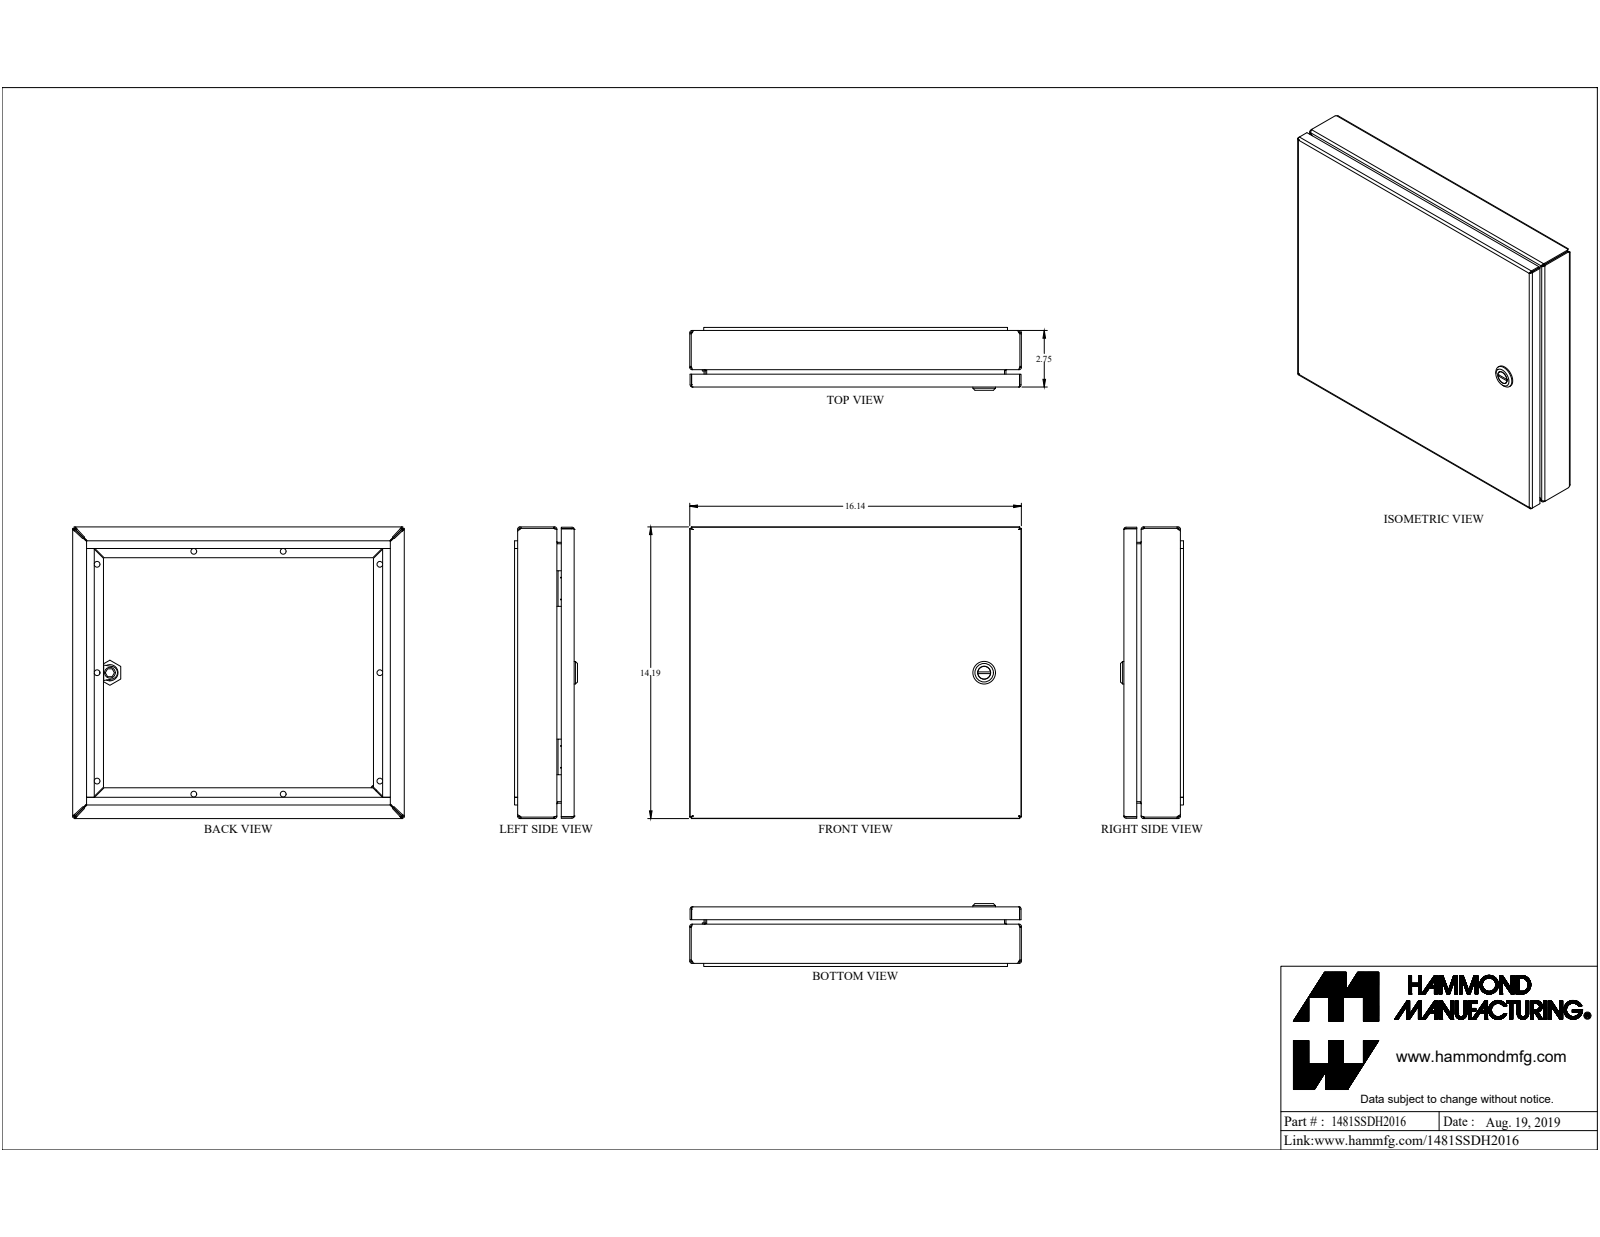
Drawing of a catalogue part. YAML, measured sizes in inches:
part_name: "1481SSDH2016"
step_written_by: "SolidWorks 2019 (CONFIG_CONTROL_DESIGN)"
units: inches
bodies: {solids: 24, faces: 618, planar: 374, cylindrical: 147, other: 97}
overall_size: [18.19, 12.14, 3.06]
volume: 49.07
surface_area: 1278
round_holes:
  - {diameter: 0.281, count: 8}
  - {diameter: 0.172, count: 1}
  - {diameter: 0.197, count: 1}
  - {diameter: 0.24, count: 1}
  - {diameter: 0.242, count: 1}
  - {diameter: 0.387, count: 1}
  - {diameter: 0.5, count: 1}
  - {diameter: 0.63, count: 1}
  - {diameter: 0.768, count: 1}
round_bosses_or_shafts:
  - {diameter: 1.1, count: 1}
  - {diameter: 0.785, count: 1}
  - {diameter: 0.625, count: 1}
  - {diameter: 0.525, count: 1}
  - {diameter: 0.475, count: 1}
  - {diameter: 0.398, count: 1}
  - {diameter: 0.356, count: 1}
  - {diameter: 0.313, count: 1}
partial_cylinders:
  - {radius: 0.036, count: 28}
  - {radius: 0.108, count: 28}
  - {radius: 0.006, count: 4}
  - {radius: 0.062, count: 4}
  - {radius: 0.25, count: 4}
  - {radius: 0.499, count: 4}
  - {radius: 0.125, count: 2}
  - {radius: 0.021, count: 1}
face_to_face_distances: [0.072, 2.578, 0.842, 1.736, 2.65, 12.068, 2.506, 2.678, 1.836, 0.1]
hole_center_spacings: [4.923, 15.946, 9.764, 7.273, 7.273, 9.293, 9.293, 12.175]
